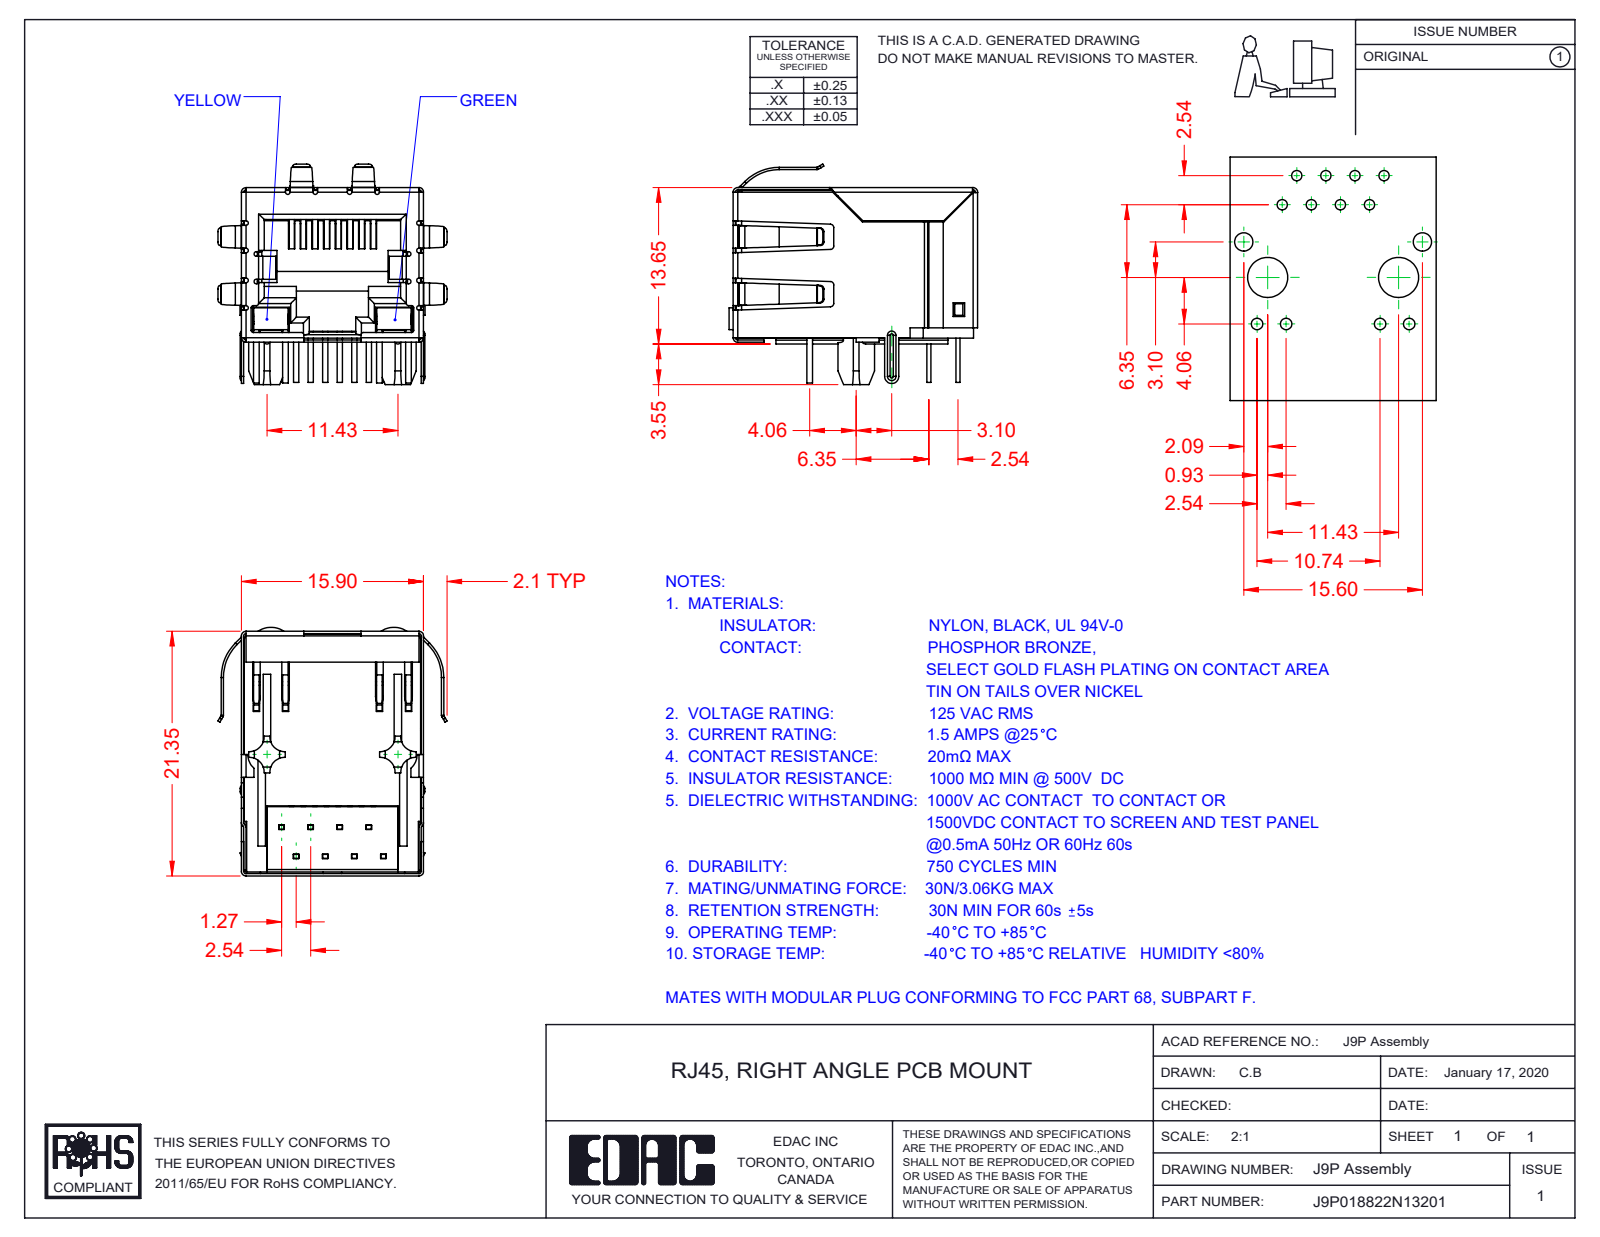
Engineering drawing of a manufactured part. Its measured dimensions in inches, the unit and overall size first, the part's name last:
Units: inches
Overall size (bounding box): 0.854 × 0.787 × 0.758
Partial cylindrical surfaces — rounded edges, fillets, slot ends (radius × count): R0.008 ×39, R0.02 ×22, R0.012 ×20, R0.016 ×16, R0.051 ×8, R0.009 ×5, R0.004 ×4, R0.012 ×4
Main face-to-face distances: 0.608, 0.618, 0.616, 0.014, 0.021, 0.61, 0.487, 0.024, 0.055, 0.023
Volume: 0.164 in³ · Surface area: 11.65 in²
Bodies: 13 solids, 1472 faces (1042 planar, 336 cylindrical, 94 other)
Part name (STEP PRODUCT): 9P-LED Contact Lock; 9P-LED LED RH_3-Green; 9P-LED Assembly; 9P-LED Insulator (+4 more)
STEP written by: SolidWorks 2016 (CONFIG_CONTROL_DESIGN)
